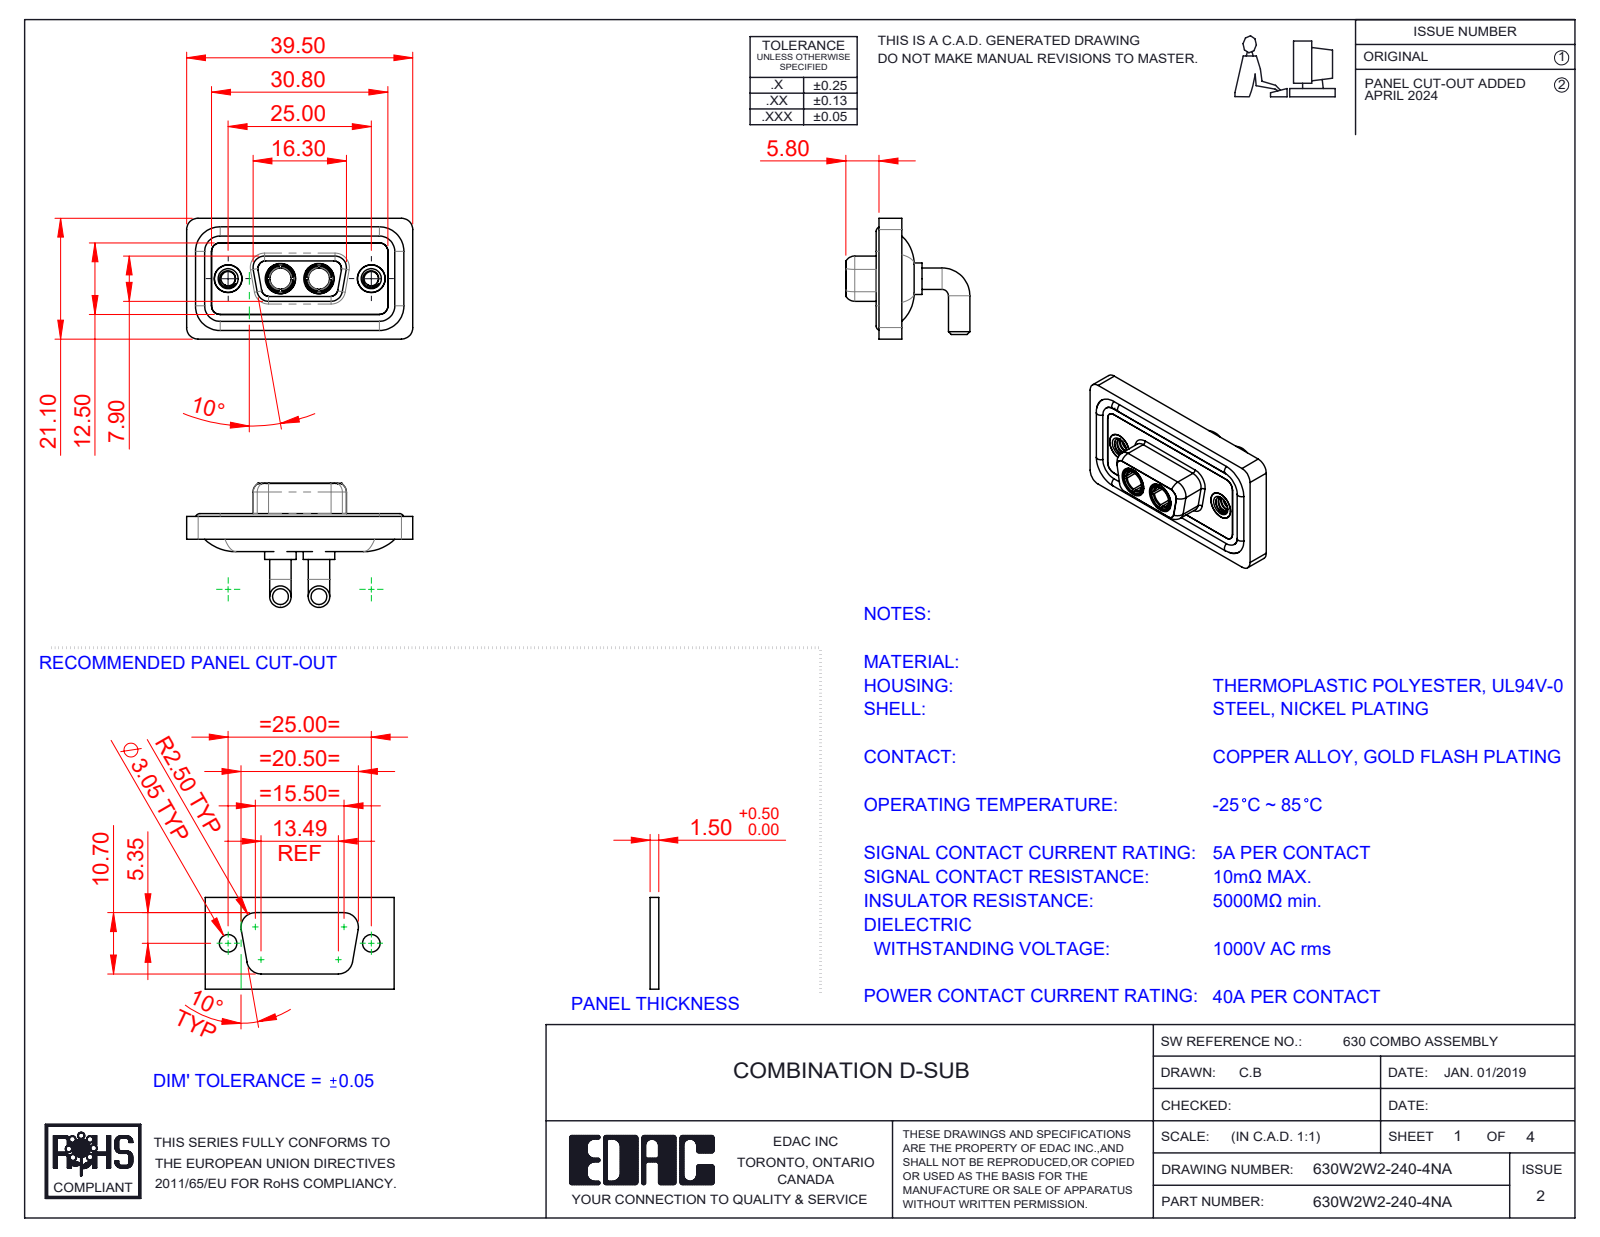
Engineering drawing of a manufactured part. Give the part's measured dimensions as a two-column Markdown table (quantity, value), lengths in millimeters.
| quantity | value |
| --- | --- |
| part name | 630Combo Shell Rear_09 Contacts; Power Socket_40A RA; 630Combo Waterproof Housing_09 Contacts; 630Combo Threaded Rivet_A (+3 more) |
| STEP written by | SolidWorks 2023 (CONFIG_CONTROL_DESIGN) |
| units | millimeters |
| bodies | 11 solids, 536 faces (163 planar, 236 cylindrical, 137 other) |
| overall size | 39.5 × 21.68 × 21.1 |
| volume | 4 954 mm³ |
| surface area | 7 876 mm² |
| round holes (diameter × count) | 4.85 × 4, 2.5 × 2, 3.7 × 2, 4 × 2, 4.05 × 2, 5 × 2, 5.3 × 2 |
| round bosses / shafts (diameter × count) | 3.75 × 4, 1.6 × 4, 5.5 × 2, 5.2 × 2, 4.96 × 2, 4.95 × 2, 4.8 × 2, 4.75 × 2 |
| partial cylindrical surfaces (radius × count) | 1.5 × 18, 2 × 18, 1.35 × 8, 1.6 × 8, 0.25 × 4, 0.5 × 4, 0.6 × 4, 0.65 × 4 |
| main face-to-face distances | 0.4, 1.8, 1.1, 2.9, 2.5, 1.6, 3.1, 2.1, 3.7, 1.5 |
| hole center spacings | 9.14, 15.86, 6.72, 25 |
